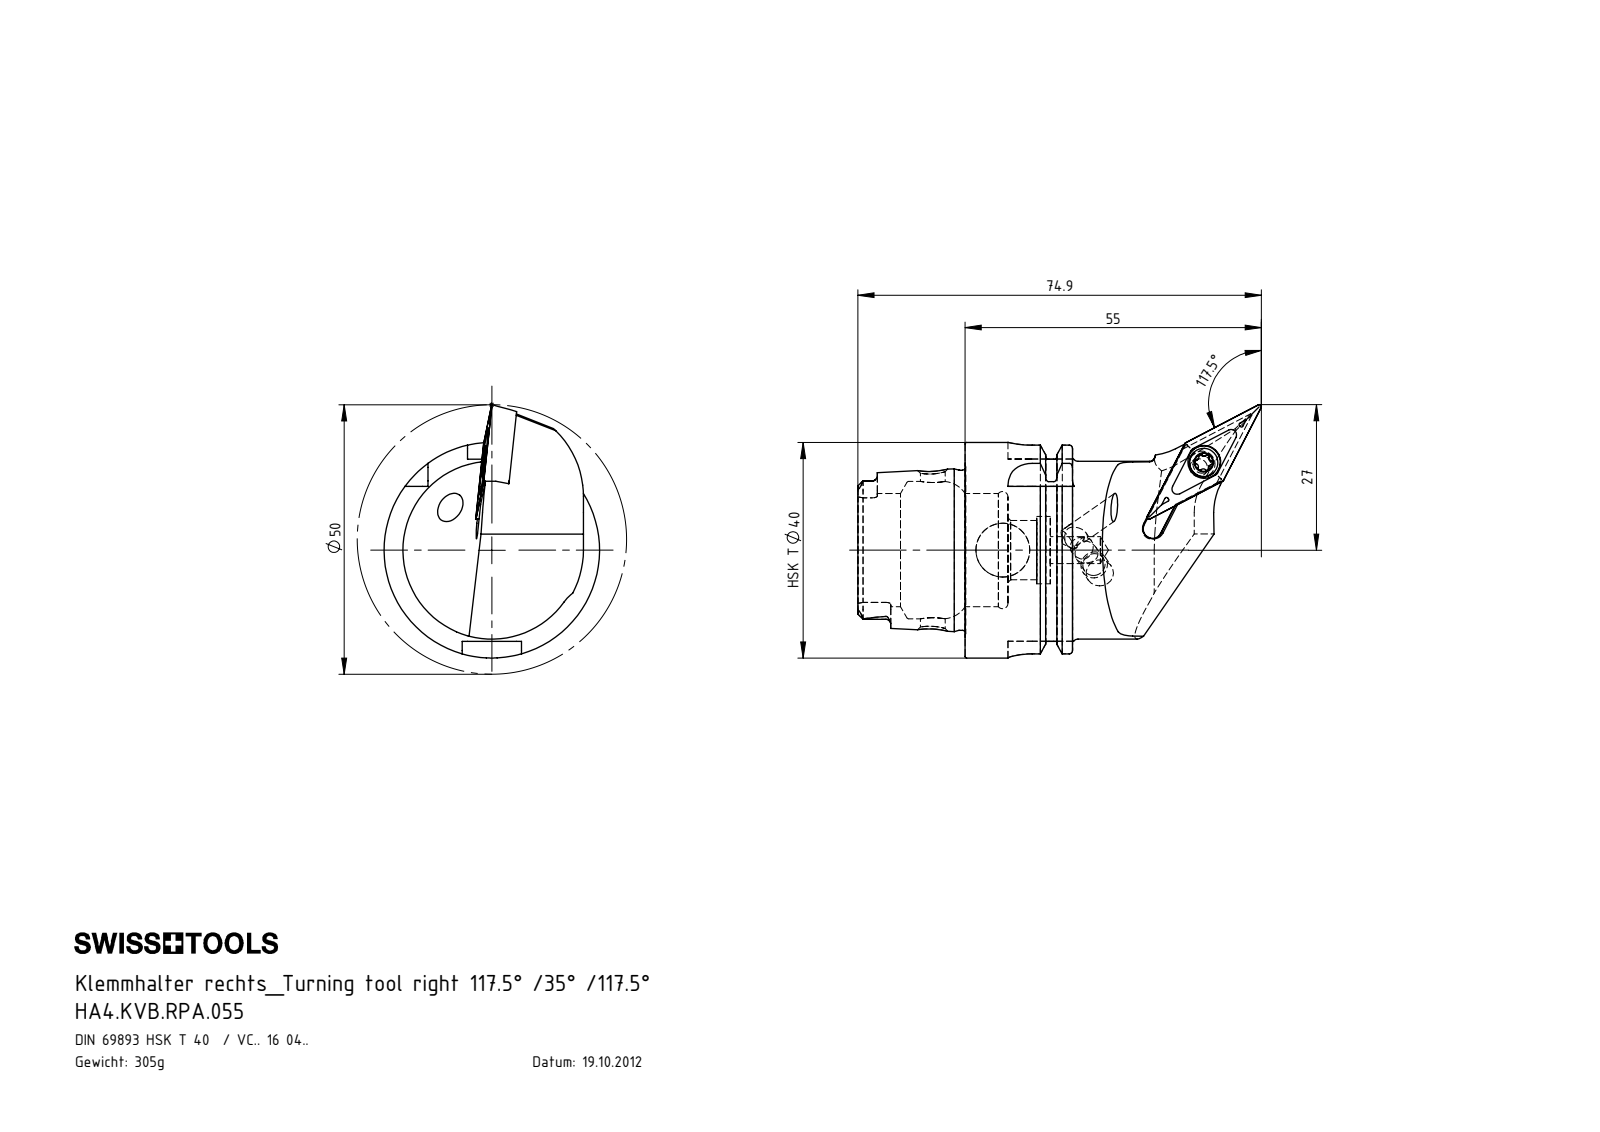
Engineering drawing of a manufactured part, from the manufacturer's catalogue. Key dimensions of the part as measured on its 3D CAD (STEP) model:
Part name (STEP PRODUCT): HA4.KVB.RPA.055; VCMT160404; HA4-KVB.RPA.055_B_Fertigbearbeitung; KVT_MB_600_050 (+1 more)
STEP written by: SolidWorks 2017 (AUTOMOTIVE_DESIGN)
Units: millimetres
Bodies: 5 solids, 318 faces (80 planar, 90 cylindrical, 148 other)
Overall size (bounding box): 74.9 × 47 × 40
Volume: 37 479 mm³ · Surface area: 13 374 mm²
Round holes (diameter × count): ⌀4.2 ×2, ⌀5 ×2, ⌀3.3 ×1, ⌀4 ×1, ⌀4.4 ×1, ⌀4.6 ×1, ⌀6.1 ×1, ⌀10 ×1, ⌀11 ×1, ⌀12.5 ×1, ⌀21 ×1, ⌀25.5 ×1
Round bosses / shafts (diameter × count): ⌀40 ×1, ⌀34.75 ×1, ⌀33 ×1, ⌀29.71 ×1, ⌀5.25 ×1, ⌀5 ×1, ⌀4 ×1
Partial cylindrical surfaces — rounded edges, fillets, slot ends (radius × count): R0.34 ×6, R0.59 ×6, R0.9 ×6, R4.5 ×4, R1.82 ×2, R1.88 ×2, R17 ×2, R1.75 ×1
Main face-to-face distances: 4.45, 7.95, 19.95, 12, 19.9, 27.85, 39.85, 35.7, 15.8, 7.85
